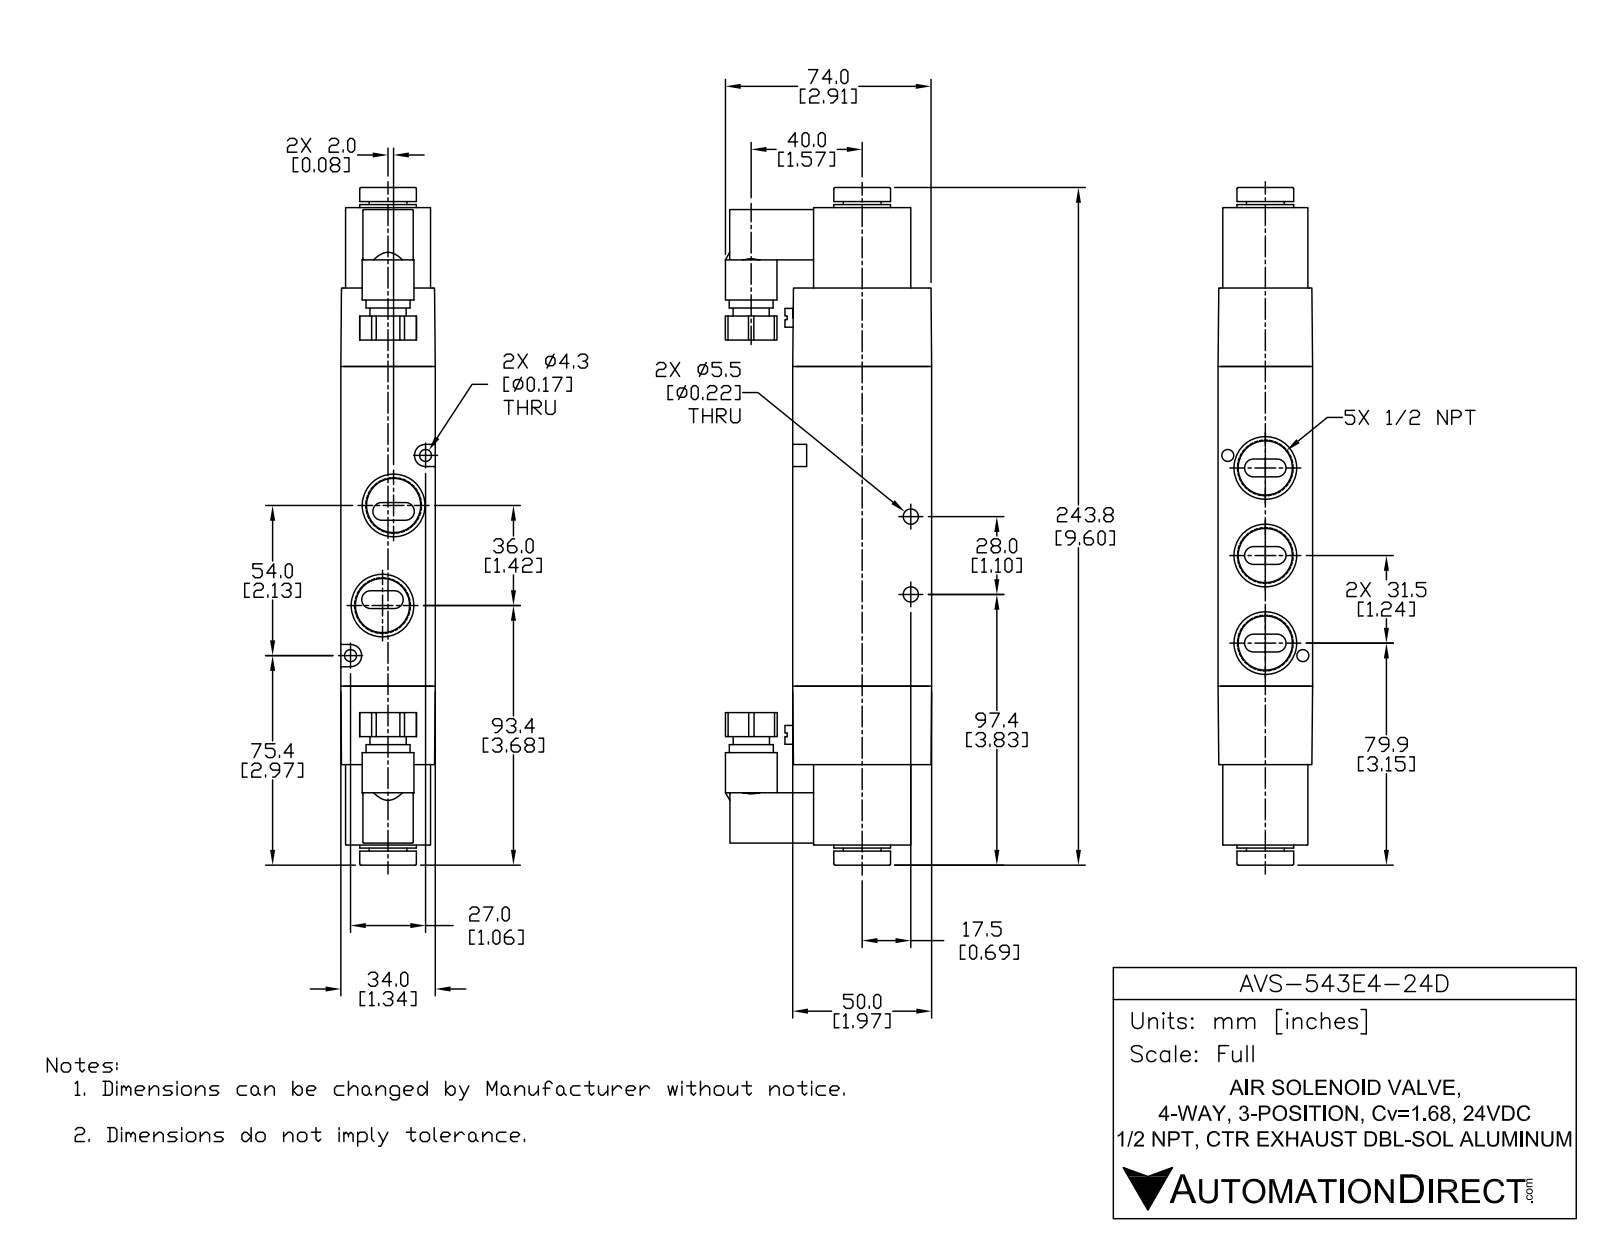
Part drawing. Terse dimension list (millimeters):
name: AVS-543E4-24D
written by: SolidWorks 2015 (CONFIG_CONTROL_DESIGN)
unit: mm
bodies: 5 solids, 248 faces (111 planar, 103 cylindrical, 34 other)
size: 243.8 × 74.2 × 34
volume: 356 277 mm³; area: 64 523 mm²
holes: 5× ⌀17.86, 2× ⌀4.3, 2× ⌀5.5, 1× ⌀9.3
bosses: 2× ⌀6.7, 1× ⌀20.8, 1× ⌀20.4, 1× ⌀18.6, 1× ⌀15.8, 1× ⌀13.6, 1× ⌀13
rounds: 18× R1.5, 10× R1, 10× R3.2, 2× R4
face distances: 34, 115, 50, 35.96, 28.2, 32.14, 51.96, 7.95, 26.05, 18.1
hole spacings: 13.65, 14.23, 18.11, 21.36, 31.5, 38.45, 49.54, 56.18
